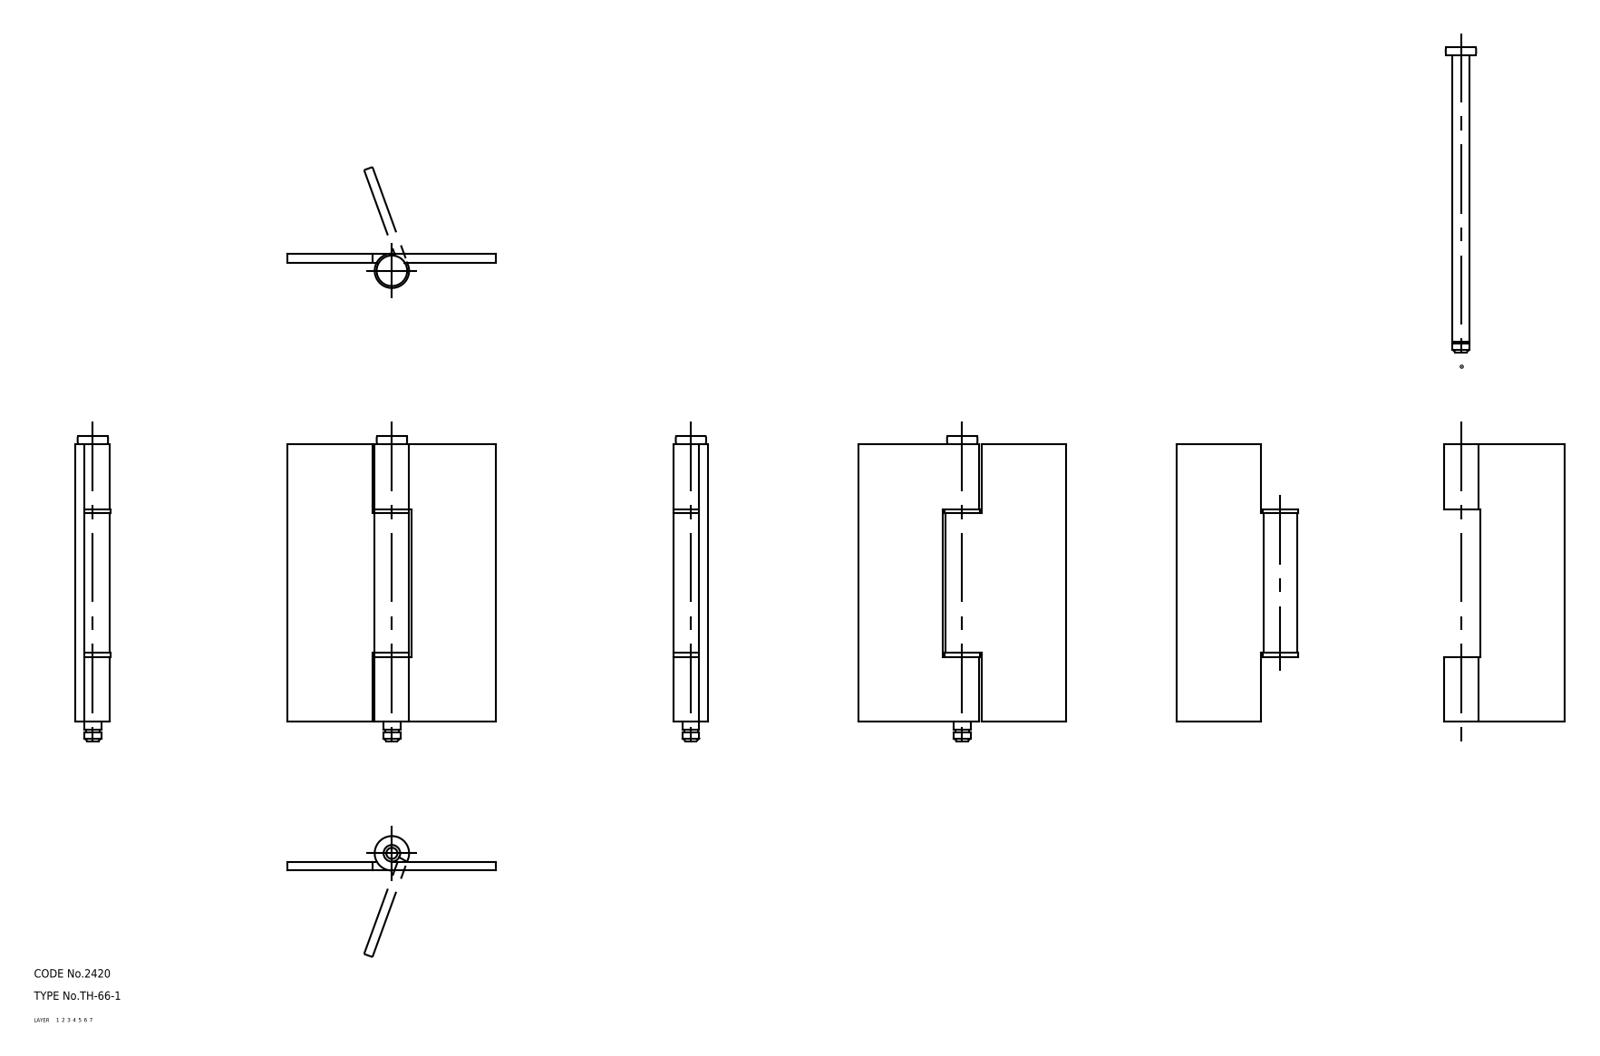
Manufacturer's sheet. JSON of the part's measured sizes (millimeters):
{"part_name": "washer; shaft; hinge piece_B; hinge piece_A (+1 more)", "step_written_by": "CADfix (AUTOMOTIVE_DESIGN)", "units": "millimeters", "bodies": {"solids": 5, "faces": 52, "planar": 0, "cylindrical": 0, "other": 52}, "overall_size": [110, 75, 12.5], "volume_mm3": 32707, "surface_area_mm2": 23323}
